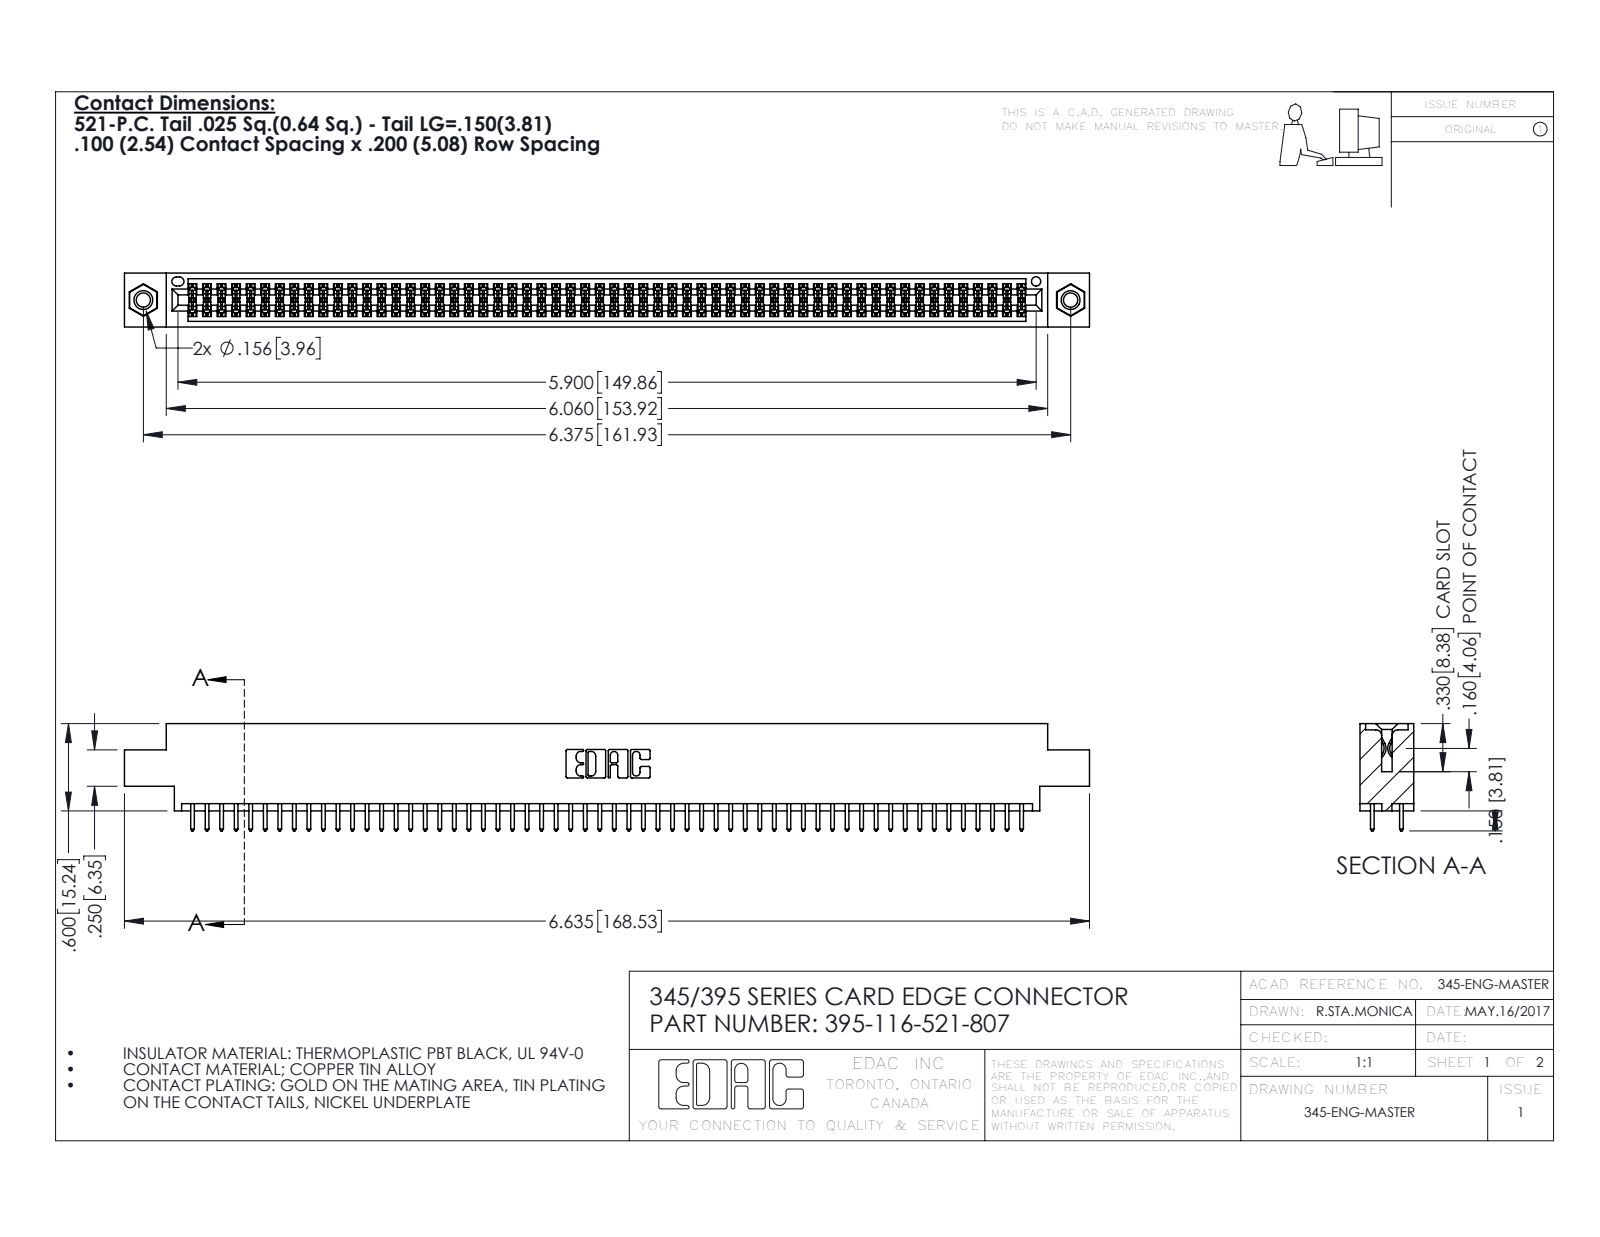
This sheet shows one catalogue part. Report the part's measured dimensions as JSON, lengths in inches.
{"part_name": "395-116-521-807; 345 Part_0.170 Offset - 0.156 Dia-TI; 345-250-001_345-250-005-103; 345-292-001_345-293-121", "step_written_by": "SolidWorks 2016 (CONFIG_CONTROL_DESIGN)", "units": "inches", "bodies": {"solids": 119, "faces": 5990, "planar": 3944, "cylindrical": 2030, "other": 16}, "overall_size": [6.635, 0.737, 0.37], "volume_in3": 0.997, "surface_area_in2": 37.72, "round_holes": [[0.098, 2], [0.125, 2], [0.156, 2], [0.064, 1]], "round_bosses_or_shafts": [[0.155, 2]], "partial_cylinders_radius": [[0.006, 174], [0.01, 116], [0.01, 22], [0.007, 6], [0.031, 6], [0.026, 3], [0.014, 2], [0.019, 2]], "face_to_face_distances": [0.072, 0.298, 0.2, 0.37, 0.098, 0.272, 0.025, 0.225, 0.175, 0.149], "hole_center_spacings": [0.27, 6.139, 6.375]}
